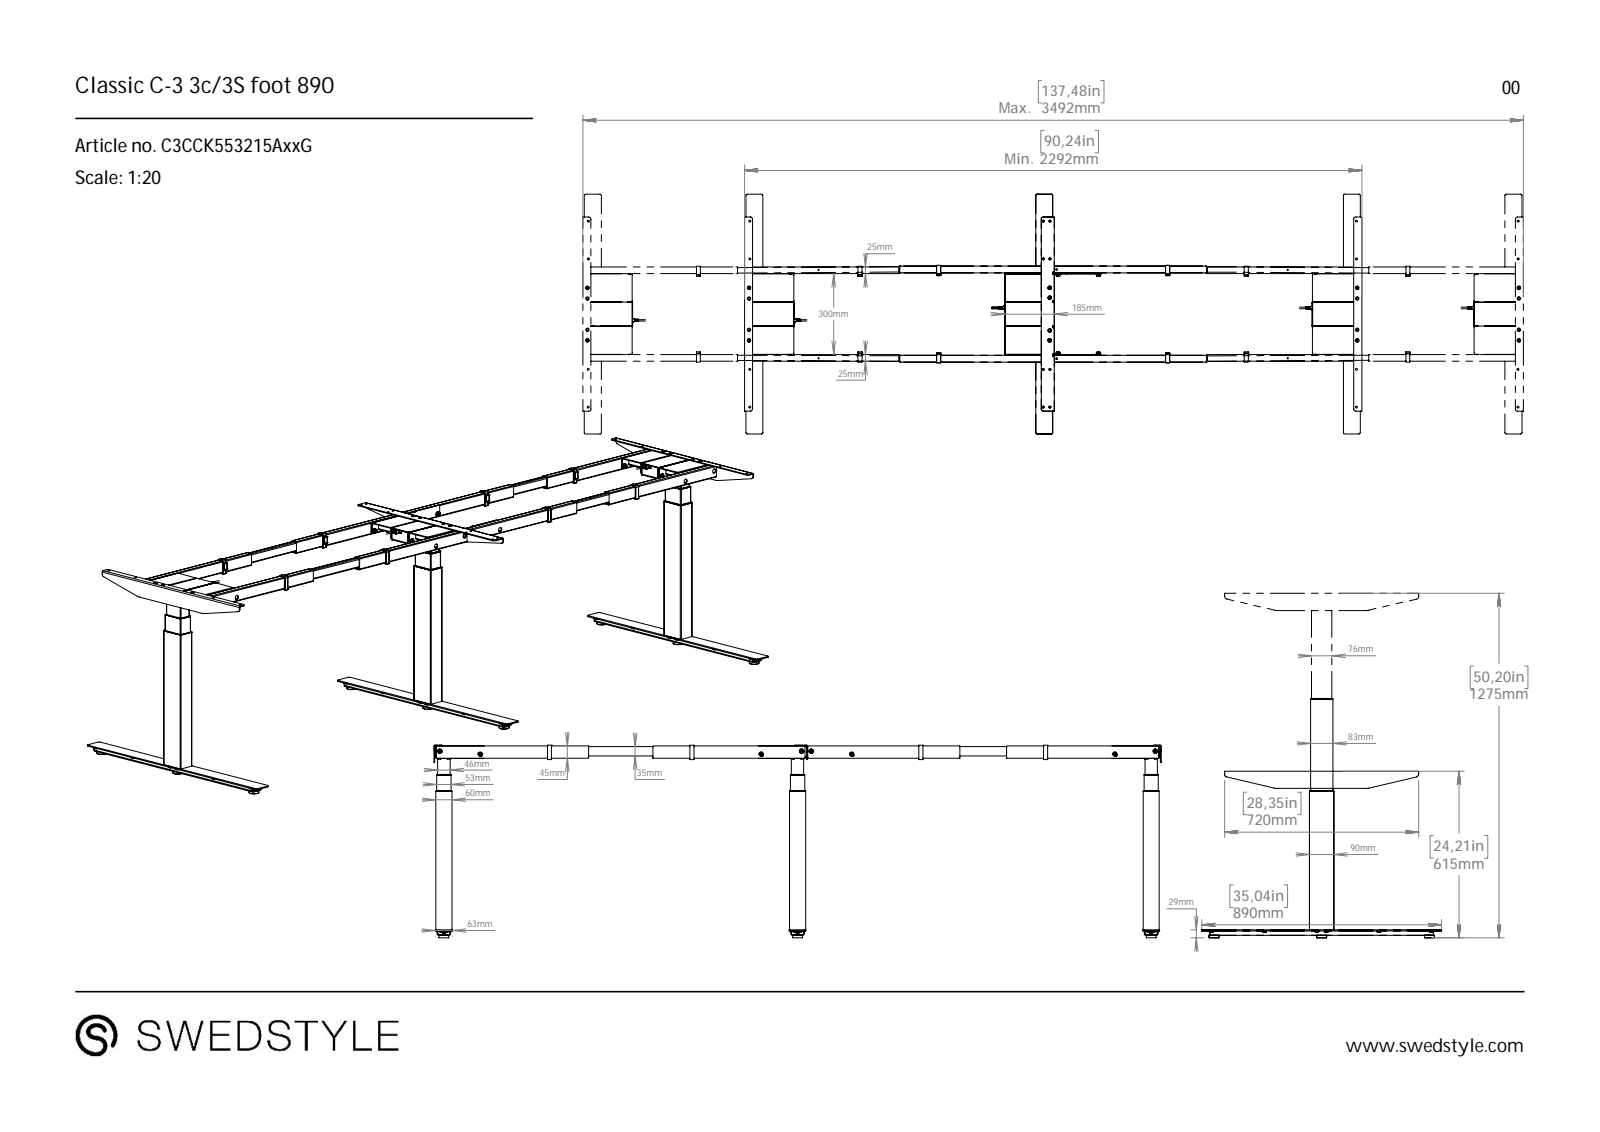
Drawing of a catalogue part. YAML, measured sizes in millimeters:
part_name: "C3CCK553215AxxG Classic C-3 3c_3S foot 890"
step_written_by: "SolidWorks 2021 (CONFIG_CONTROL_DESIGN)"
units: millimeters
bodies: {solids: 0, faces: 1866, planar: 876, cylindrical: 548, other: 442}
overall_size: [2700, 890, 715]
round_holes:
  - {diameter: 16, count: 19}
  - {diameter: 7, count: 13}
  - {diameter: 5.4, count: 6}
  - {diameter: 4.2, count: 2}
  - {diameter: 7.5, count: 2}
  - {diameter: 8, count: 1}
round_bosses_or_shafts:
  - {diameter: 11.65, count: 4}
  - {diameter: 6, count: 4}
  - {diameter: 8, count: 3}
  - {diameter: 15.57, count: 2}
  - {diameter: 8.5, count: 2}
  - {diameter: 5.5, count: 2}
partial_cylinders:
  - {radius: 2.5, count: 82}
  - {radius: 0.5, count: 34}
  - {radius: 3, count: 34}
  - {radius: 5, count: 25}
  - {radius: 2.8, count: 24}
  - {radius: 3.5, count: 16}
  - {radius: 1.5, count: 13}
  - {radius: 4.5, count: 12}
face_to_face_distances: [3.5, 2, 3, 1313, 7, 53, 20, 1316.5, 1309.5, 2.5]
hole_center_spacings: [1313, 1313.44, 22, 34, 40.5, 140, 550, 188.1]
